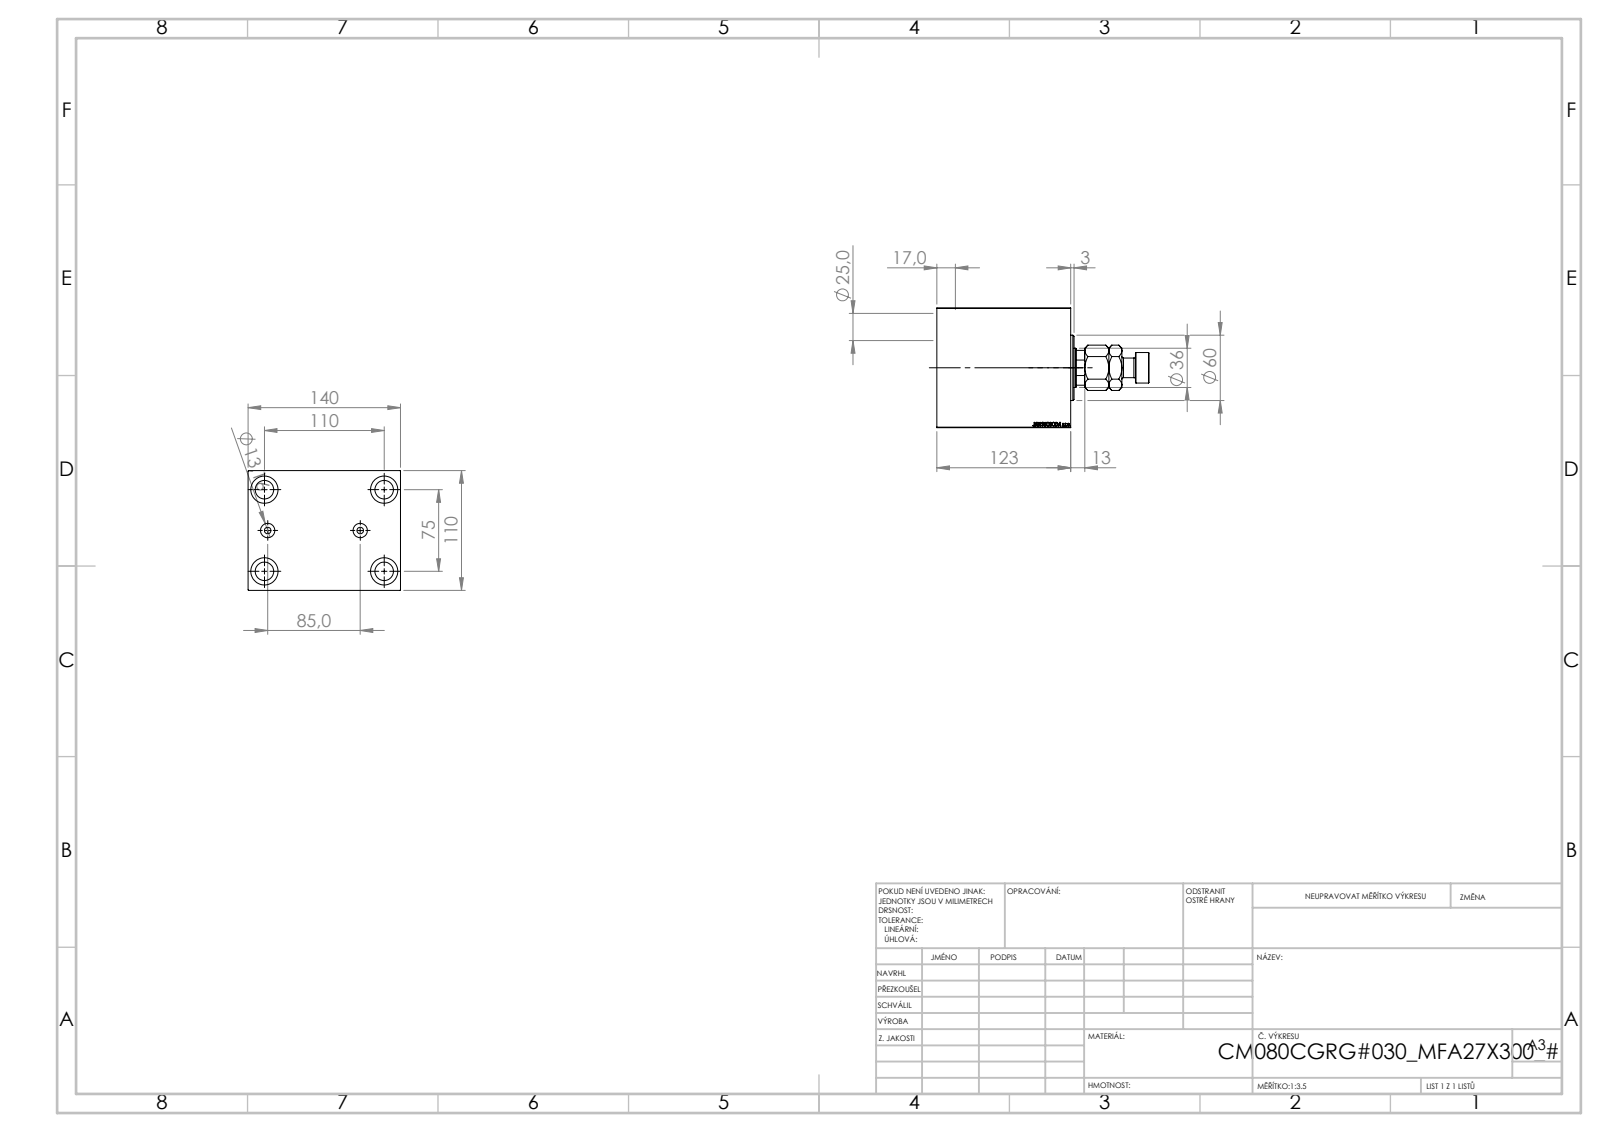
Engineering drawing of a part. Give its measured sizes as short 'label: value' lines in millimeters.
name: V450CM_C_VCP; V450CM_VC_B; MFA; V450CM_C_Body
written by: SolidWorks 2019 (CONFIG_CONTROL_DESIGN)
unit: mm
bodies: 4 solids, 915 faces (427 planar, 62 cylindrical, 426 other)
size: 196 × 140 × 110
volume: 1 667 000 mm³; area: 187 868 mm²
holes: 4× ⌀17, 4× ⌀25, 2× ⌀6, 2× ⌀13.16, 1× ⌀25.5, 1× ⌀36, 1× ⌀39.5, 1× ⌀80, 1× ⌀82, 1× ⌀87
bosses: 1× ⌀60, 1× ⌀28, 1× ⌀18
rounds: 1× R17.5
face distances: 110, 140, 123, 63.25, 59.75, 113, 10, 83, 53.25, 40
hole spacings: 39.53, 66.57, 104.46, 42.5, 75, 110, 133.14, 85
